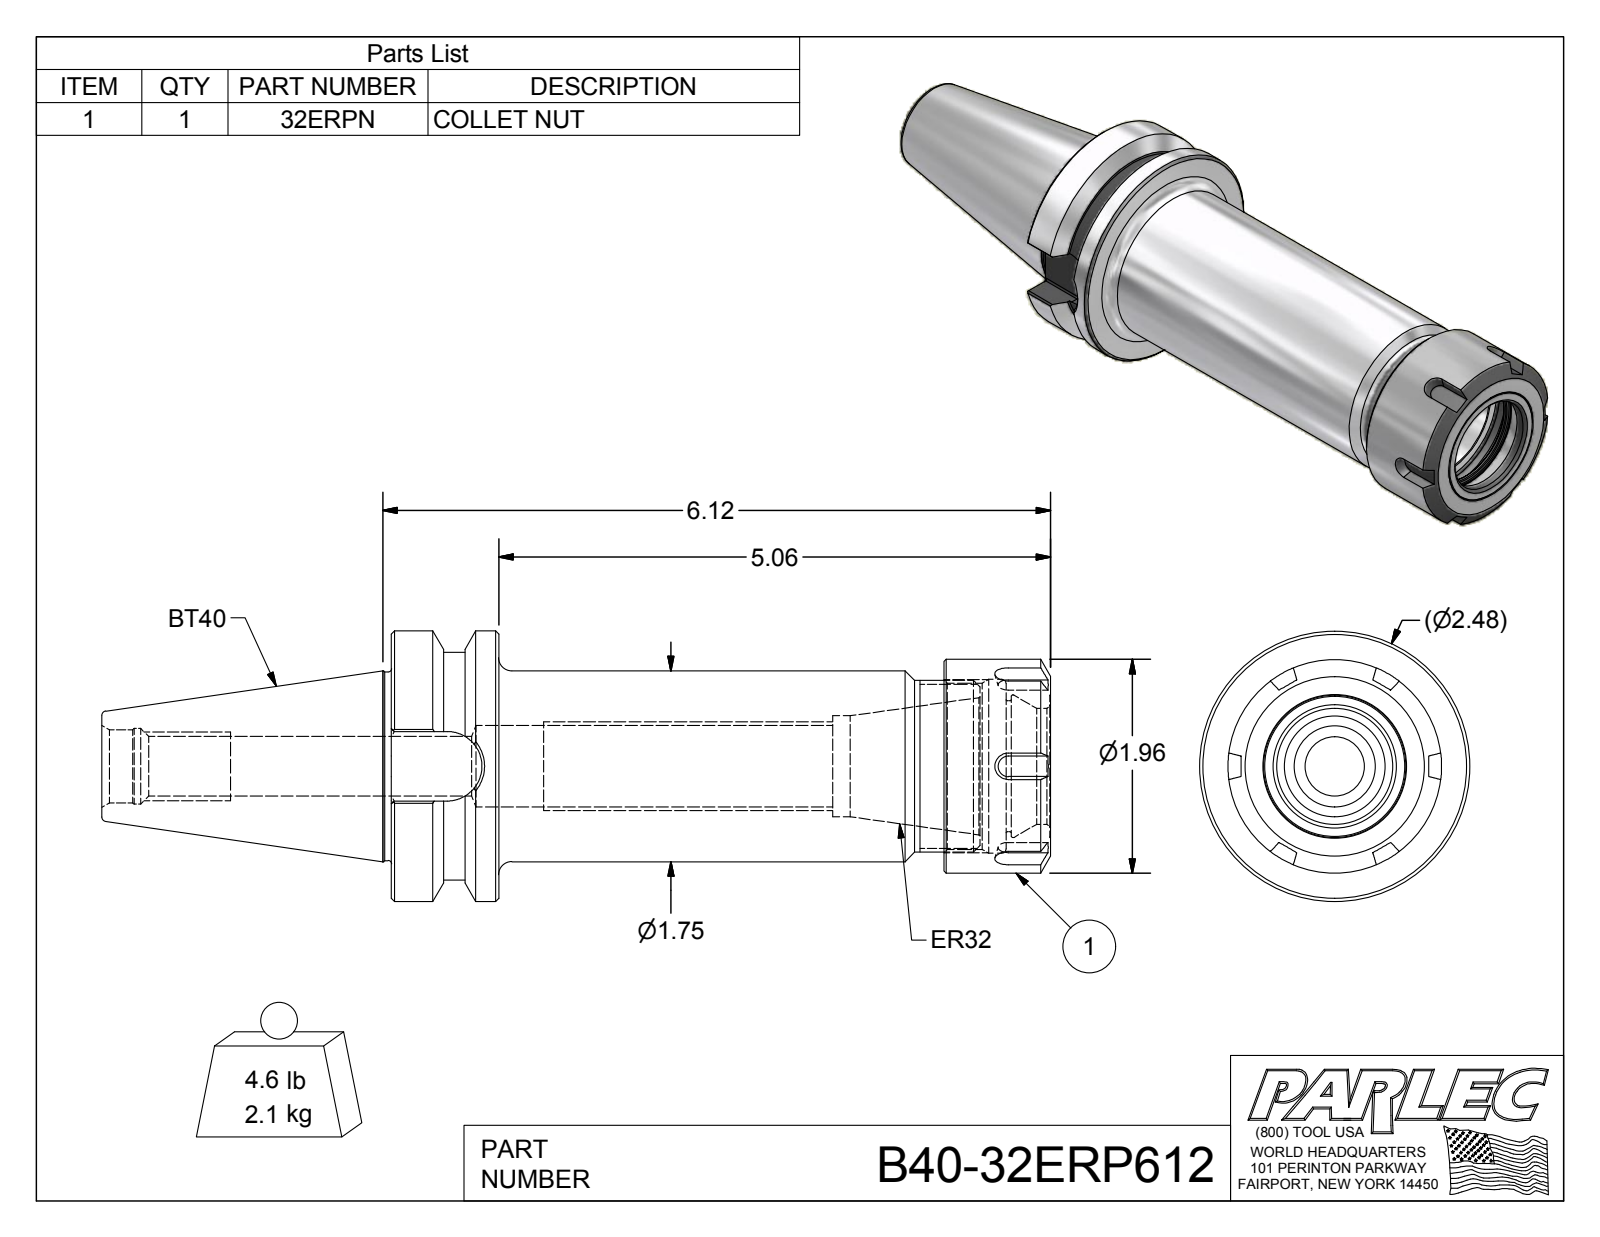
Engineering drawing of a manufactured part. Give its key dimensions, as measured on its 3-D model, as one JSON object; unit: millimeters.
{"part_name": "B40-32ERP612; B40-32ER6-1; 32ERPN", "step_written_by": "Autodesk Inventor 2012 (AUTOMOTIVE_DESIGN)", "units": "millimeters", "bodies": {"solids": 2, "faces": 119, "planar": 47, "cylindrical": 29, "other": 43}, "overall_size": [220.9, 63, 63], "volume_mm3": 267600, "surface_area_mm2": 53860, "round_holes": [[13.8, 1], [17, 1], [17.6, 1], [18.9, 1], [23.5, 1], [27, 1], [30.5, 1], [33.1, 1], [38.7, 1], [40.5, 1]], "round_bosses_or_shafts": [[63, 1], [53, 1], [49.7, 1], [44.5, 1], [43.9, 1], [40, 1]], "partial_cylinders_radius": [[0.5, 8], [8.1, 1]], "face_to_face_distances": [25, 153.5, 128.5, 128.6, 103.6, 24.8, 143.1, 118.1, 14.5, 10.3]}
